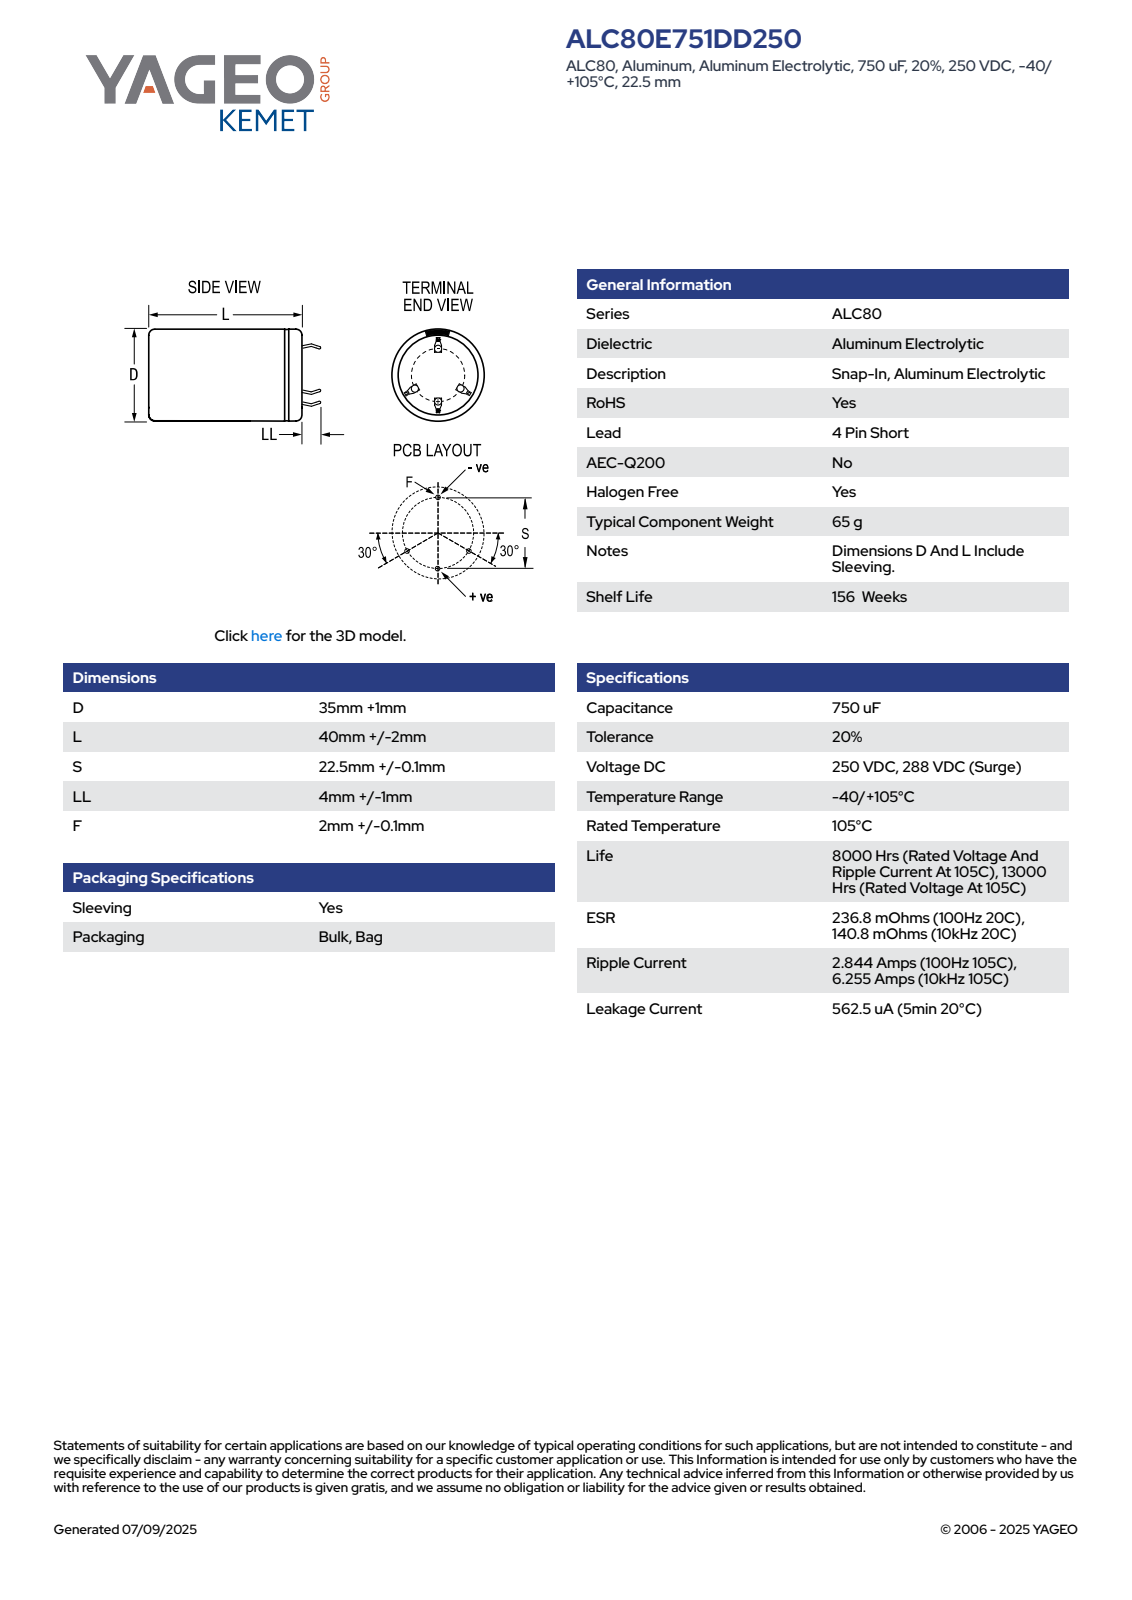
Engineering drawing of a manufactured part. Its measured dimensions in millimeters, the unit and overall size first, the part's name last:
Units: millimetres
Overall size (bounding box): 46.99 × 36 × 36
Round holes (diameter × count): ⌀31.85 ×1
Round bosses / shafts (diameter × count): ⌀36 ×1
Partial cylindrical surfaces — rounded edges, fillets, slot ends (radius × count): R17.99 ×1
Main face-to-face distances: 41.99, 42.49, 0.5, 0.6, 0.54, 0.75, 1.35, 22.23, 2.1, 22.77
Volume: 42 232 mm³ · Surface area: 6 809 mm²
Bodies: 1 solid, 134 faces (80 planar, 15 cylindrical, 39 other)
Part name (STEP PRODUCT): CARS_K4P_35X40_D36L42S22.5LL5F2.1
STEP written by: SolidWorks 2014 (AUTOMOTIVE_DESIGN)
